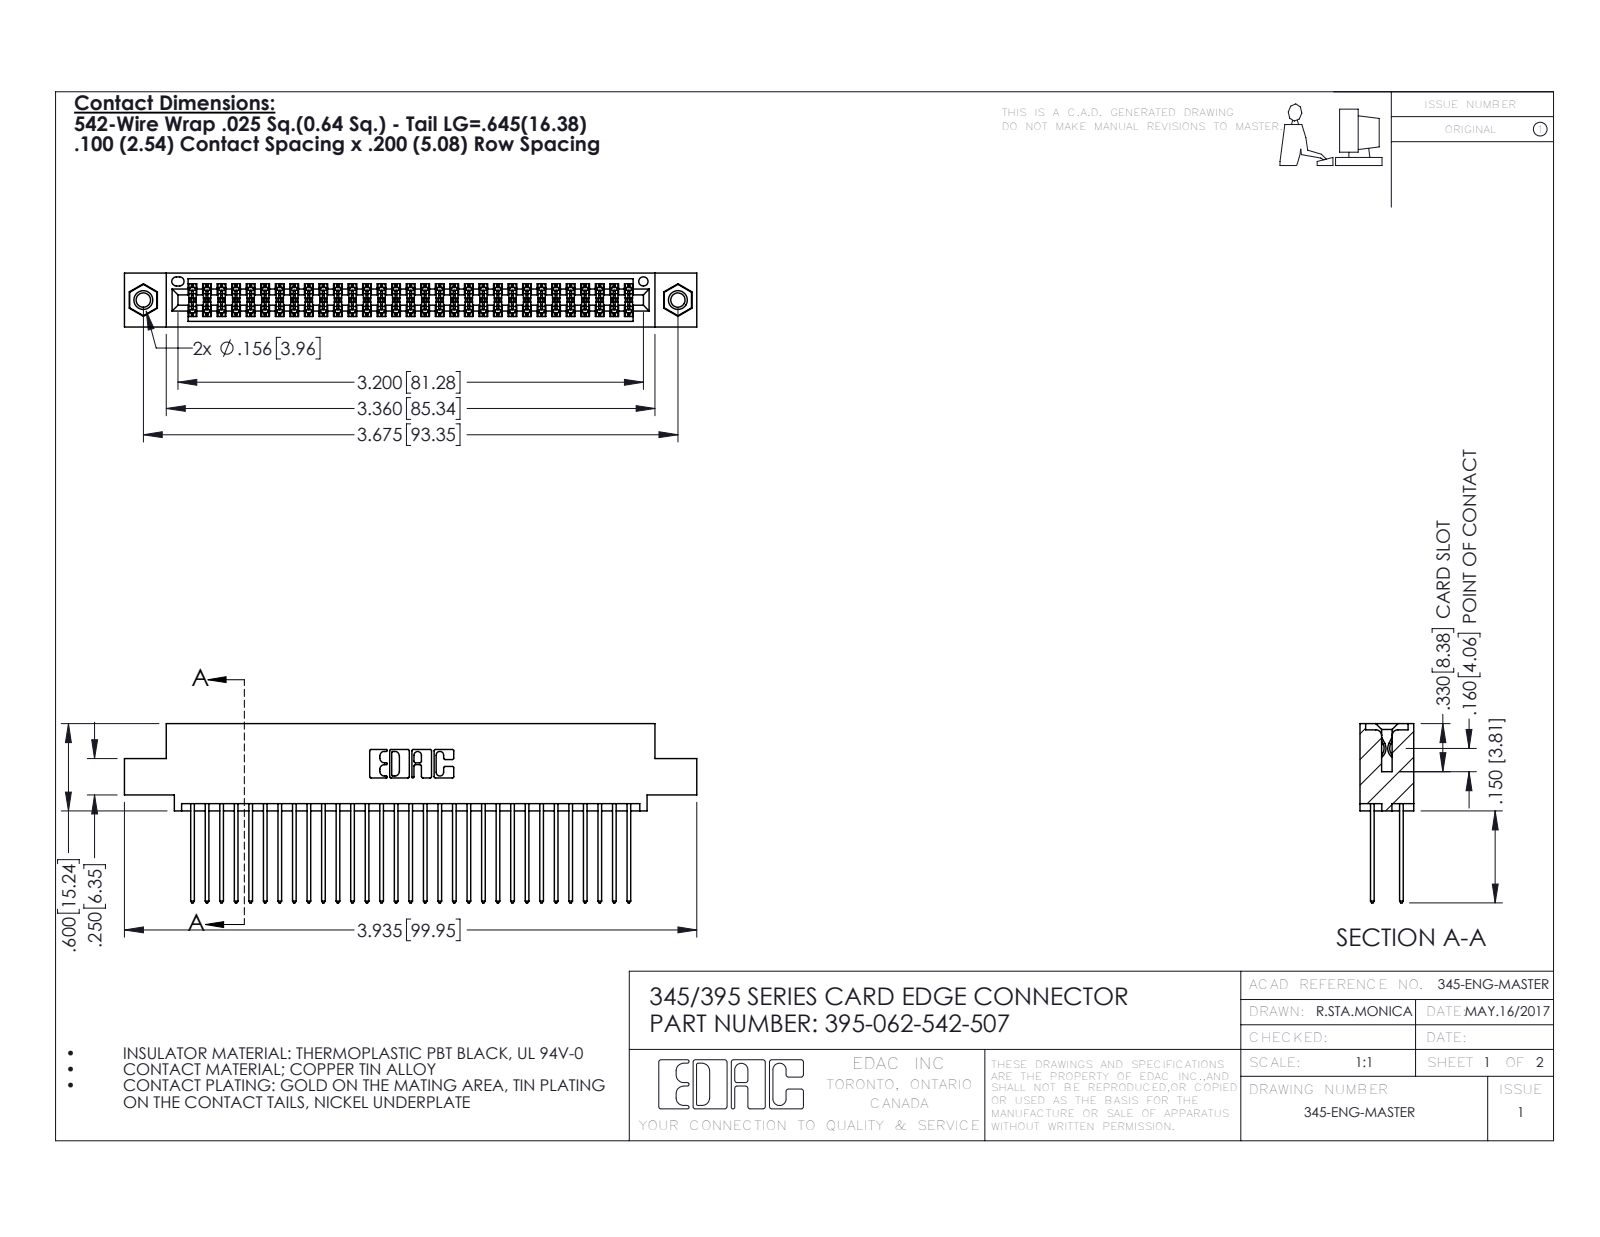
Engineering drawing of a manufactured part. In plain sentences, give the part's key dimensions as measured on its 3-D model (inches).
The part is named "395-062-542-507; 345-292-001_345-293-142; 345 Part_0.110 Offset - 0.156 Dia-TI; 345-250-001_345-250-005-103". Its 3-D file was written by "SolidWorks 2016 (CONFIG_CONTROL_DESIGN)". It is 65 solids with 3290 faces: 2162 planar, 1112 cylindrical and 16 other. Overall it measures 3.935 by 1.232 by 0.37 inches. Its volume is 0.599 cubic inches and its surface area 24.42 square inches. Round holes: 2 of diameter 0.098, 2 of diameter 0.125, 2 of diameter 0.156, 1 of diameter 0.064. Round bosses or shafts: 2 of diameter 0.155. Partial cylindrical surfaces (rounded edges, fillets, slot ends): 93 of radius 0.006, 62 of radius 0.01, 22 of radius 0.01, 6 of radius 0.007, 6 of radius 0.031, 3 of radius 0.026, 2 of radius 0.014, 2 of radius 0.019. The main face-to-face distances are 0.072, 0.298, 0.2, 0.098, 0.272, 0.025, 0.37, 0.225, 0.175, 0.149. The hole center spacings are 0.27, 3.44, 3.675.
